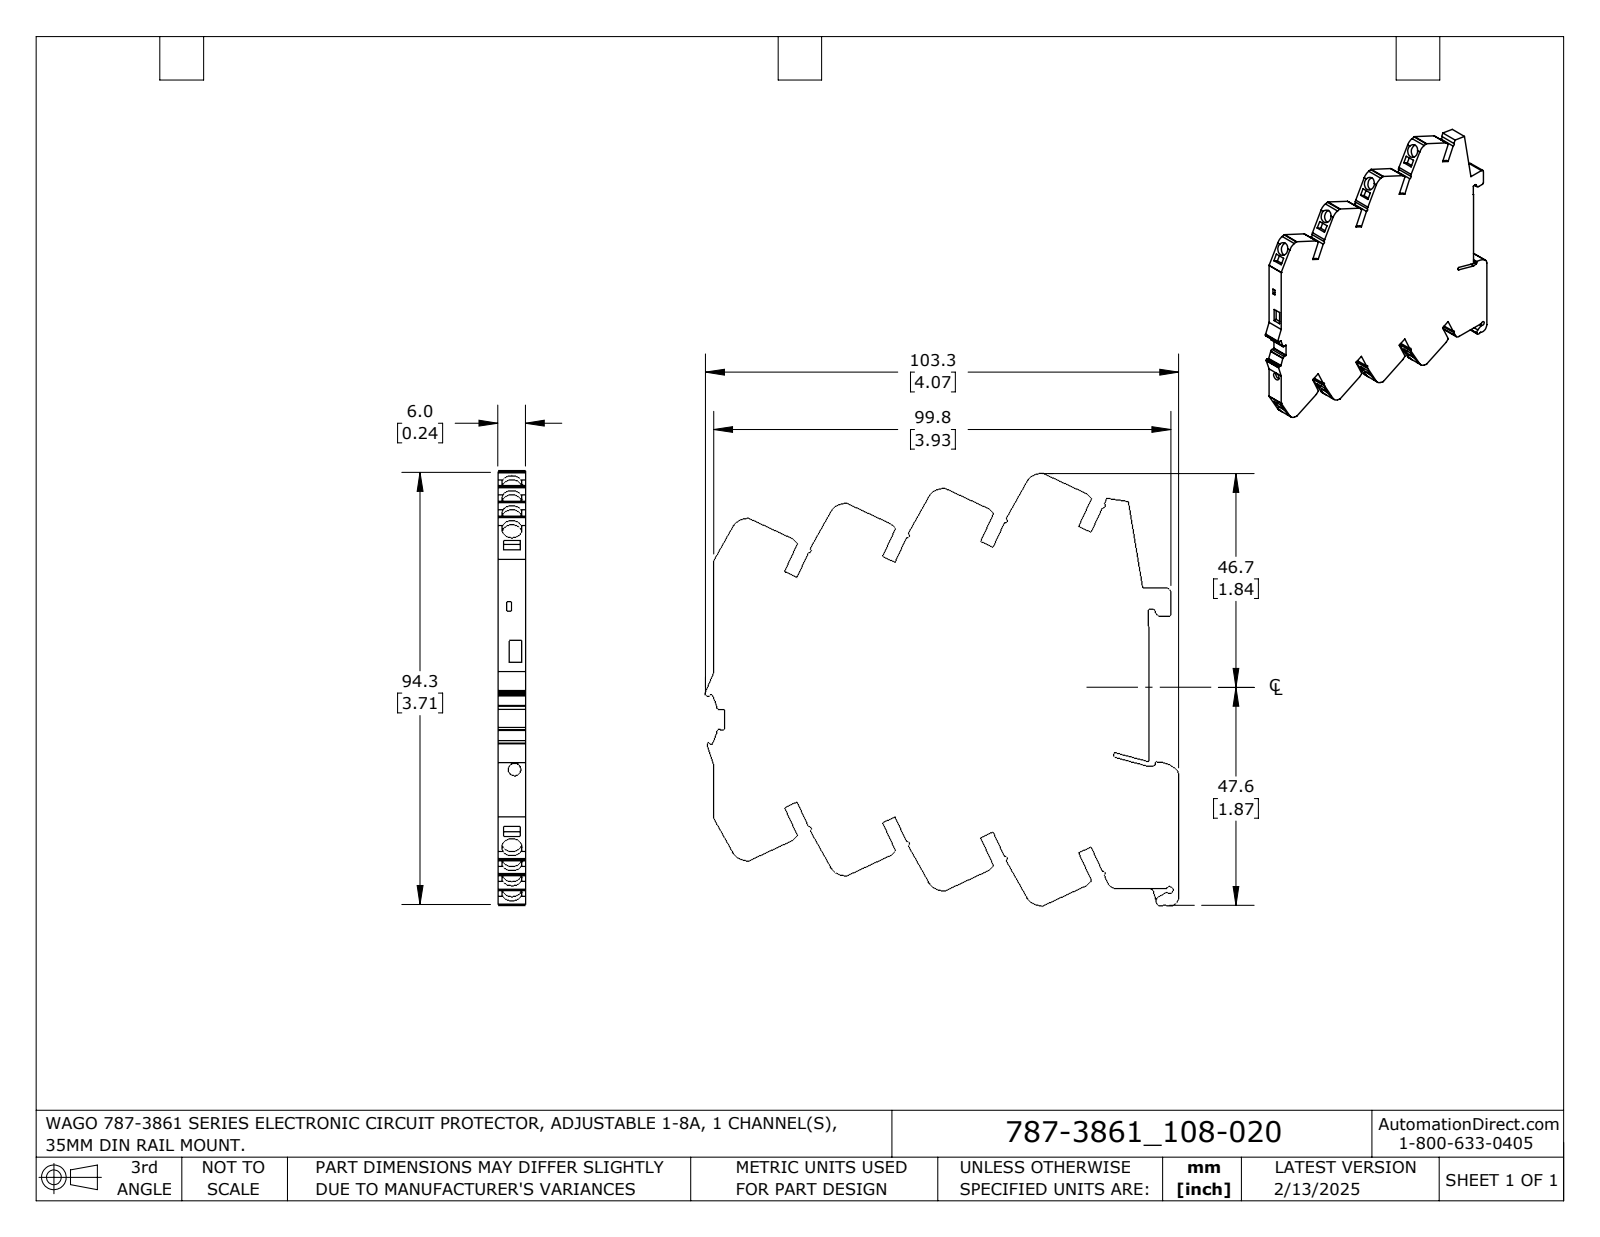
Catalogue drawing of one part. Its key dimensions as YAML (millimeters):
part_name: "787-3861_108-020_HI"
step_written_by: "SolidWorks 2024 (AUTOMOTIVE_DESIGN)"
units: millimeters
bodies: {solids: 1, faces: 267, planar: 202, cylindrical: 65, other: 0}
overall_size: [103.3, 94.26, 6]
volume: 43980
surface_area: 18879
round_holes:
  - {diameter: 4.4, count: 8}
  - {diameter: 2.7, count: 1}
partial_cylinders:
  - {radius: 0.2, count: 13}
  - {radius: 0.5, count: 12}
  - {radius: 0.4, count: 8}
  - {radius: 3.35, count: 8}
  - {radius: 1, count: 5}
  - {radius: 0.3, count: 3}
  - {radius: 2, count: 3}
  - {radius: 0.45, count: 2}
face_to_face_distances: [6, 17.99, 17.02, 12.01, 3, 35.98, 12, 24.01, 14.99, 34.04]
hole_center_spacings: [13.35, 13.34, 26.7, 26.71, 40.05]
